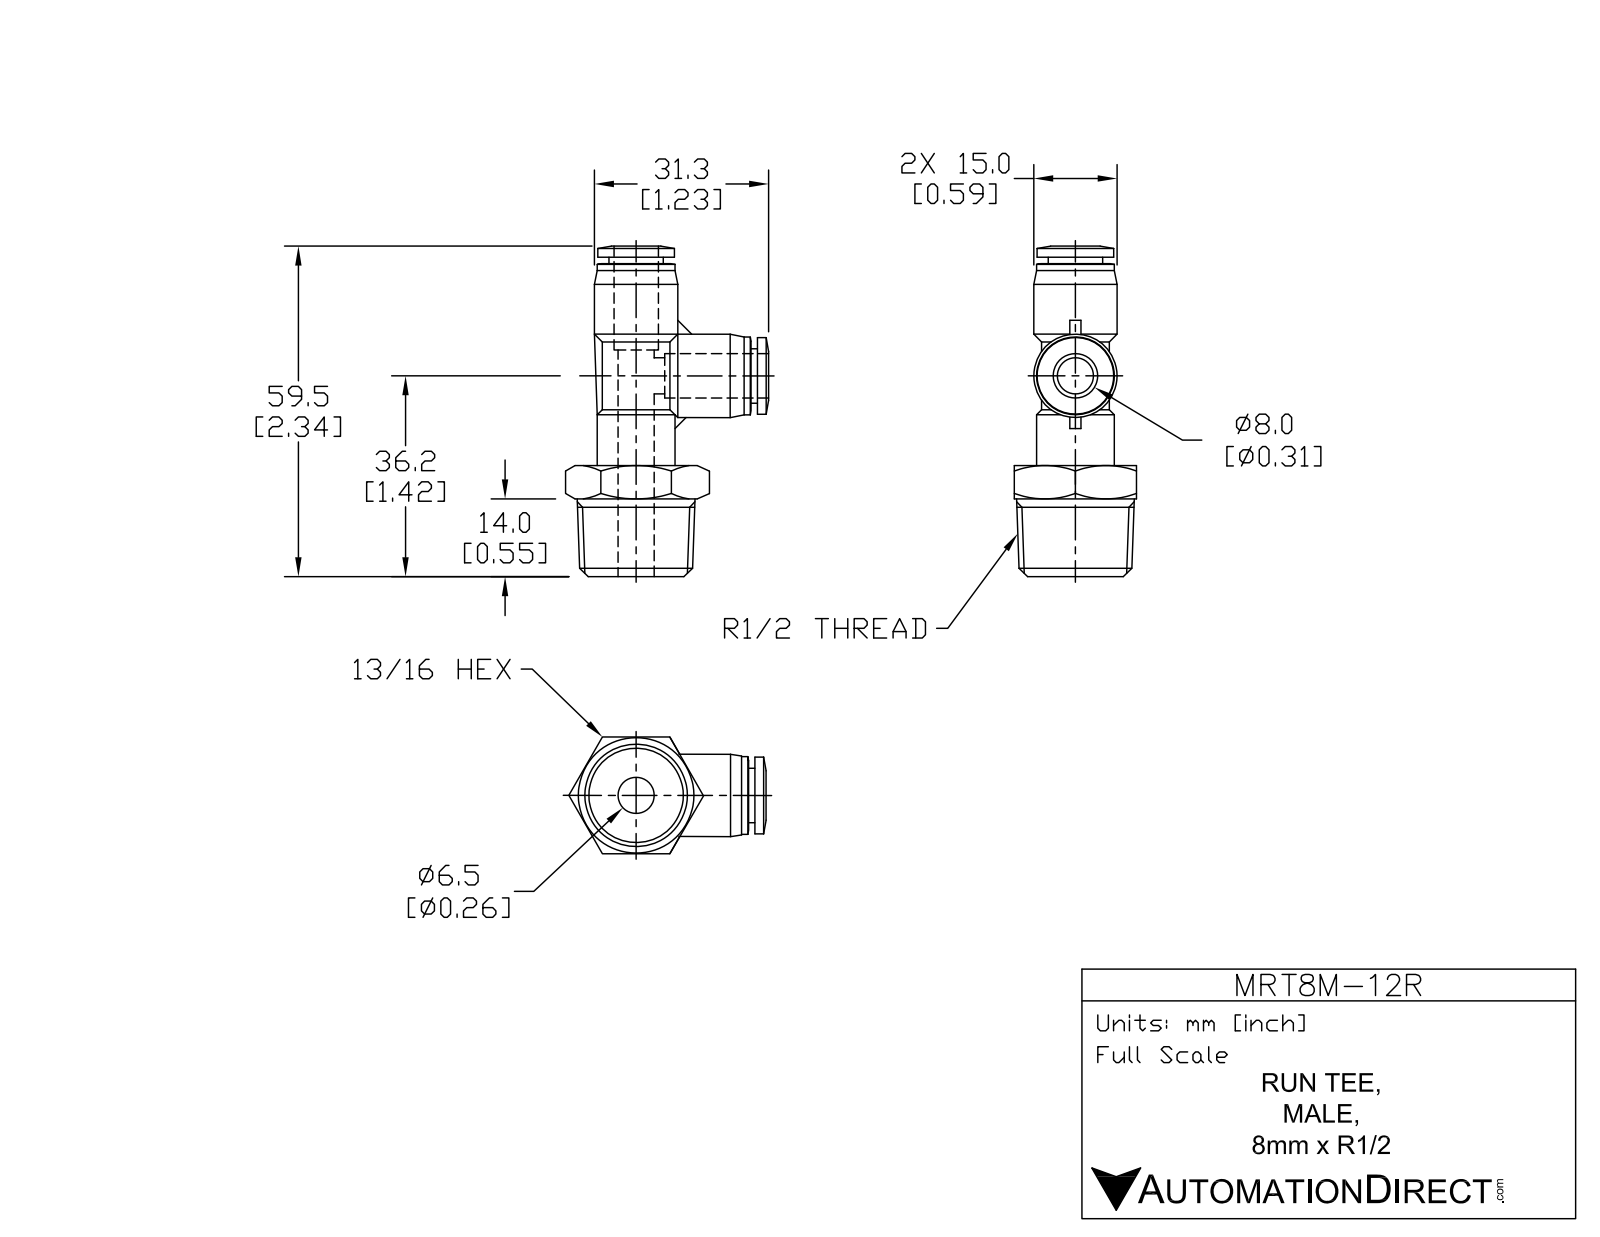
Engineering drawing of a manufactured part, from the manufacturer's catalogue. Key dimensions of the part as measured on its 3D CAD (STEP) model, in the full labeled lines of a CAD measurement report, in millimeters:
Part name (STEP PRODUCT): MRT8M-12R
STEP written by: SolidWorks 2015 (AUTOMOTIVE_DESIGN)
Units: millimetres
Bodies: 1 solid, 99 faces (24 planar, 32 cylindrical, 43 other)
Overall size (bounding box): 59.1 × 35.5 × 21
Volume: 12 300 mm³ · Surface area: 6 523 mm²
Round holes (diameter × count): ⌀6 ×2, ⌀8.3 ×2
Round bosses / shafts (diameter × count): ⌀15 ×2, ⌀14 ×2, ⌀13.8 ×2, ⌀12.2 ×2, ⌀9.8 ×2
Main face-to-face distances: 21, 20, 1.1, 57.1, 37.1, 15.1, 16.3, 56, 35.9, 9.5
